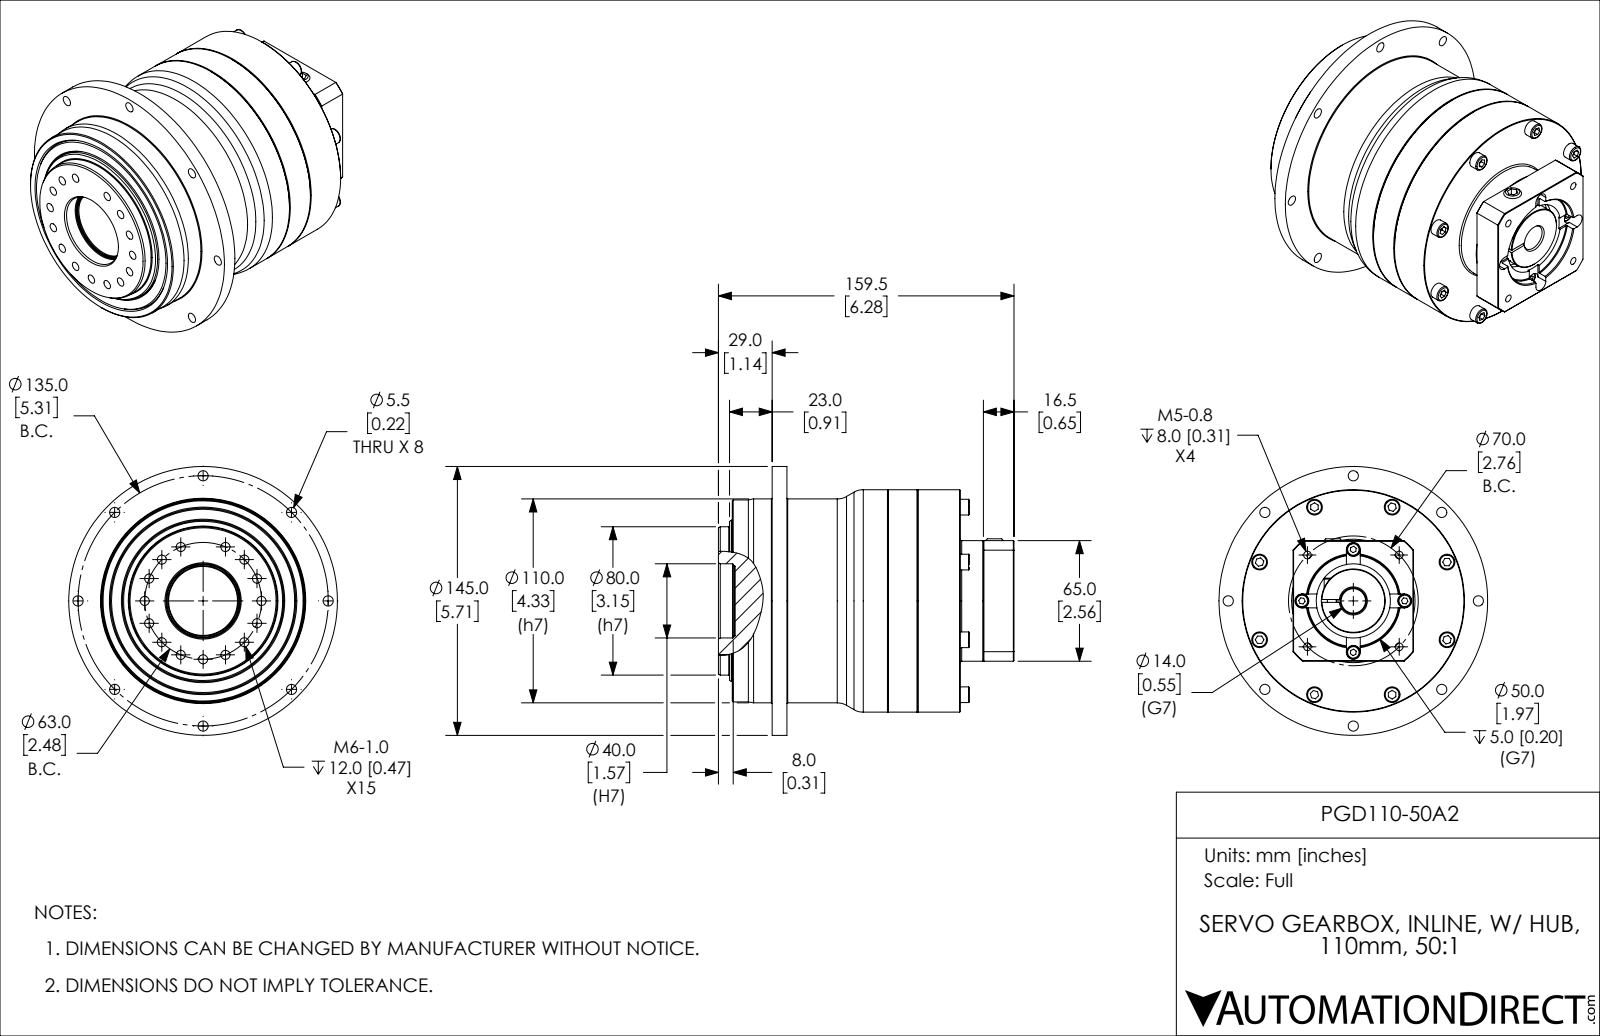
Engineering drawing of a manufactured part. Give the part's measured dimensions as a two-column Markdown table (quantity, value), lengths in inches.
| quantity | value |
| --- | --- |
| part name | PGD110-50A2 |
| STEP written by | SolidWorks 2015 (AUTOMOTIVE_DESIGN) |
| units | inches |
| bodies | 5 solids, 514 faces (247 planar, 178 cylindrical, 89 other) |
| overall size | 6.28 × 5.709 × 5.709 |
| volume | 86.29 in³ |
| surface area | 177.2 in² |
| round holes (diameter × count) | 0.194 × 11, 0.217 × 8, 0.163 × 4, 0.194 × 4, 0.295 × 4, 0.197 × 3, 0.315 × 1, 0.335 × 1, 0.551 × 1, 1.465 × 1, 1.543 × 1, 1.575 × 1 |
| round bosses / shafts (diameter × count) | 0.335 × 8, 0.276 × 4, 5.709 × 1, 4.724 × 1, 4.331 × 1, 3.15 × 1, 2.559 × 1, 1.654 × 1 |
| partial cylindrical surfaces (radius × count) | 0.187 × 1, 1.673 × 1 |
| main face-to-face distances | 0.157, 0.866, 4.922, 1.024, 4.056, 3.898, 5.198, 0.079, 1.142, 1.299 |
| hole center spacings | 1.585, 2.465, 3.335, 3.833, 0.484, 2.062, 2.933, 1.754 |
